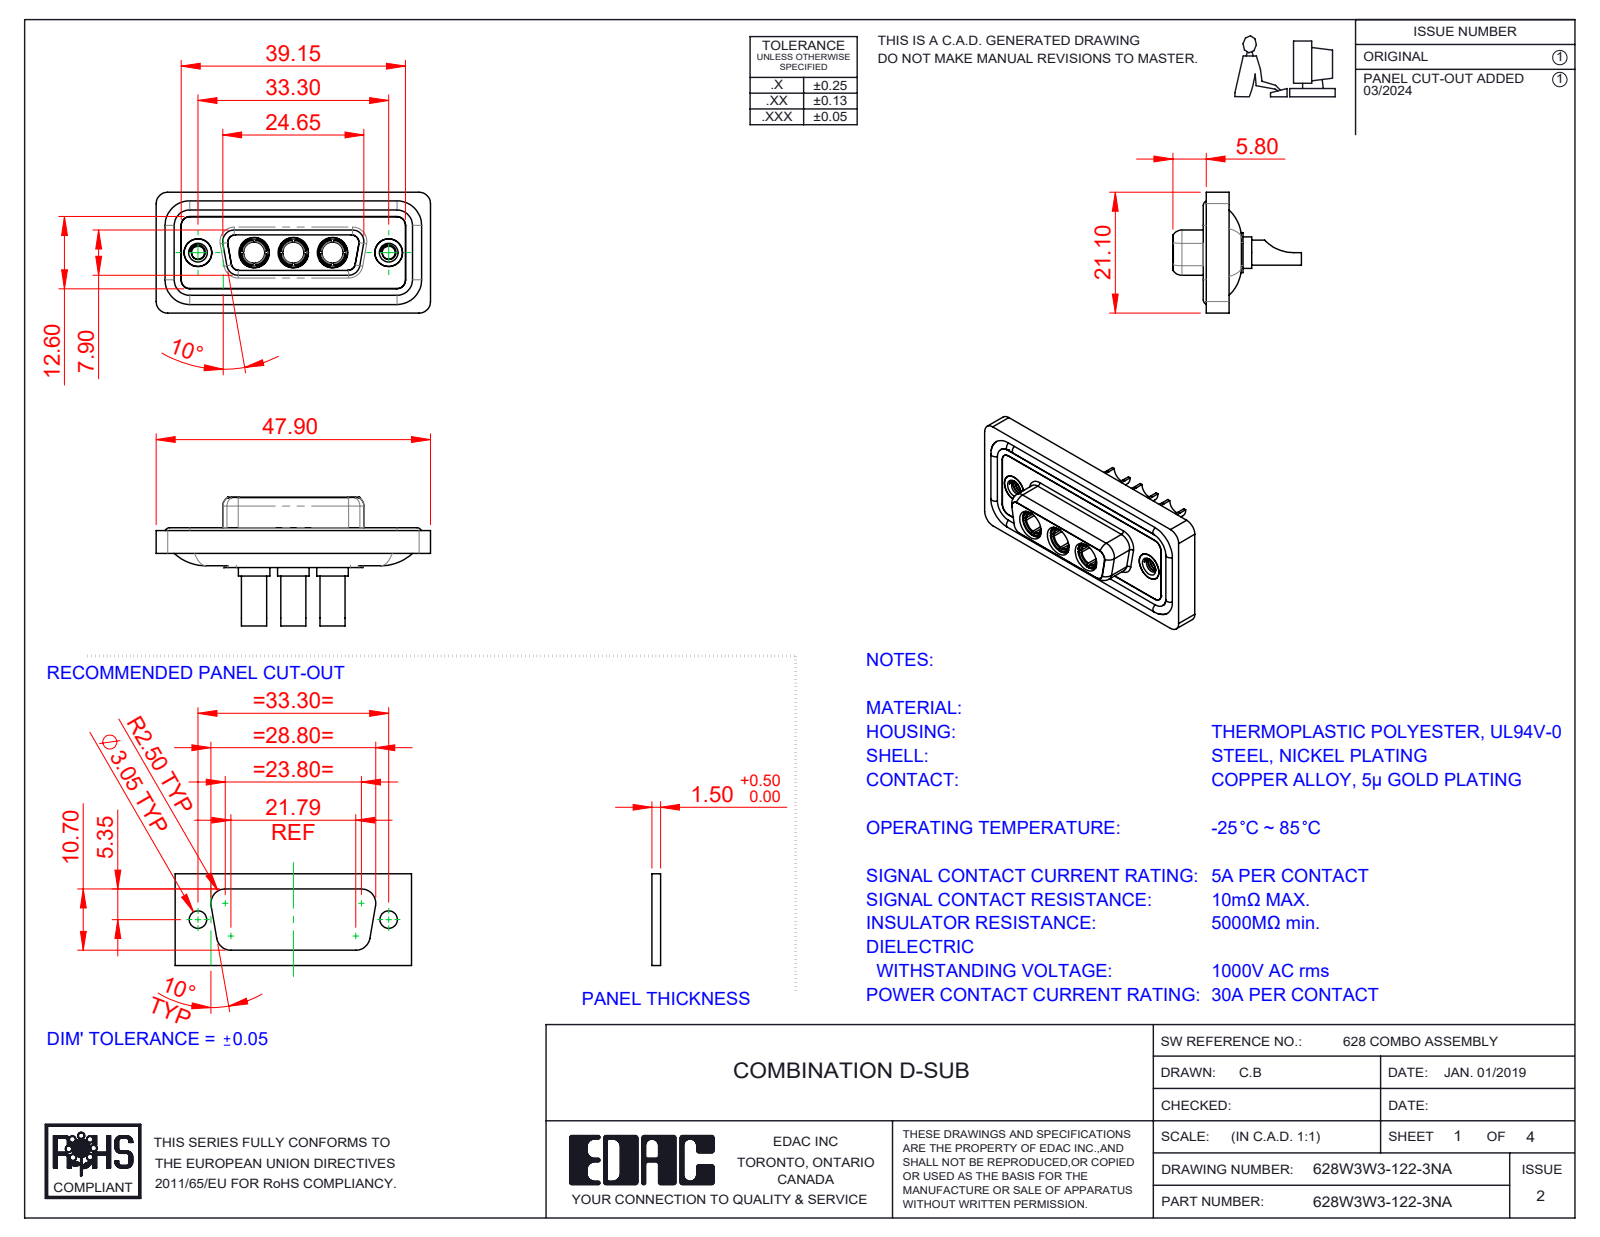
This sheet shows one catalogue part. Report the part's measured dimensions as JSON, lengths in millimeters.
{"part_name": "Power Socket_30A SC; 628Combo Threaded Rivet_A; 628W3W3-122-3NA; 628Combo Housing_3W3 (+3 more)", "step_written_by": "SolidWorks 2023 (CONFIG_CONTROL_DESIGN)", "units": "millimeters", "bodies": {"solids": 13, "faces": 624, "planar": 201, "cylindrical": 268, "other": 155}, "overall_size": [47.9, 22.45, 21.1], "volume_mm3": 6100, "surface_area_mm2": 10059, "round_holes": [[4.85, 5], [3.5, 3], [3.7, 3], [5.3, 3], [2.26, 2], [4, 2], [4.05, 2], [5, 2]], "round_bosses_or_shafts": [[1.6, 4], [5.5, 3], [5.2, 3], [4.96, 3], [4.75, 3], [4.4, 3], [3.75, 3], [4.95, 2]], "partial_cylinders_radius": [[1.5, 22], [2, 20], [1.35, 12], [1.6, 8], [0.25, 4], [0.5, 4], [0.6, 4], [0.65, 4]], "face_to_face_distances": [0.4, 1.8, 1.6, 0.5, 7.45, 1.1, 2.9, 5.65, 7.05, 6.6], "hole_center_spacings": [6.85, 9.8, 16.65, 23.5, 13.7, 33.3]}
